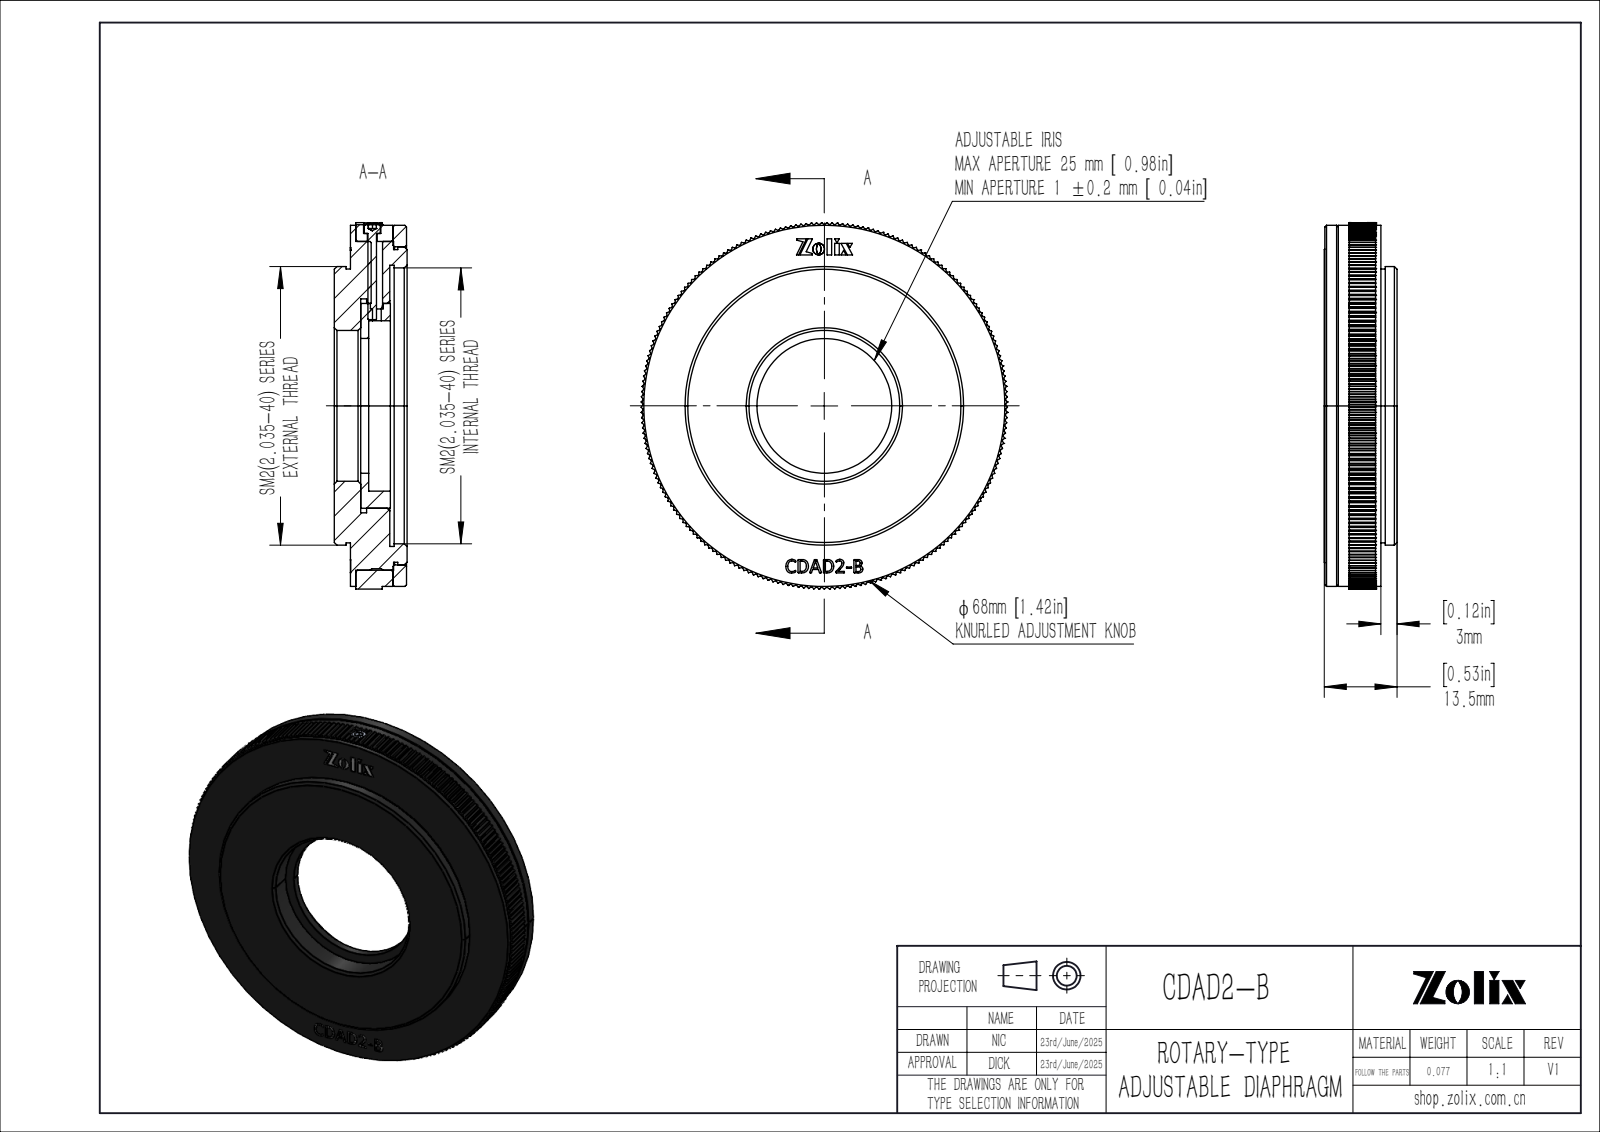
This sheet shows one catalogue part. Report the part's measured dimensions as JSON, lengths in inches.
{"part_name": "CDAD2-B", "step_written_by": "SolidWorks 2020 (CONFIG_CONTROL_DESIGN)", "units": "inches", "bodies": {"solids": 5, "faces": 1347, "planar": 708, "cylindrical": 550, "other": 89}, "overall_size": [2.677, 2.677, 0.531], "volume_in3": 1.738, "surface_area_in2": 32.16, "round_holes": [[0.063, 1], [0.071, 1], [0.126, 1], [0.984, 1], [1.102, 1], [1.244, 1], [1.496, 1], [1.563, 1], [2.016, 1], [2.055, 1], [2.323, 1]], "round_bosses_or_shafts": [[2.638, 1], [2.402, 1], [2.283, 1], [2.035, 1], [2, 1], [0.118, 1], [0.063, 1]], "partial_cylinders_radius": [[0.004, 221], [0.041, 2], [0.709, 1], [1.189, 1], [1.339, 1]], "face_to_face_distances": [0.118, 0.157, 0.193, 0.272, 0.236, 0.035, 0.075, 0.024, 0.311, 0.429], "hole_center_spacings": [0.033]}
